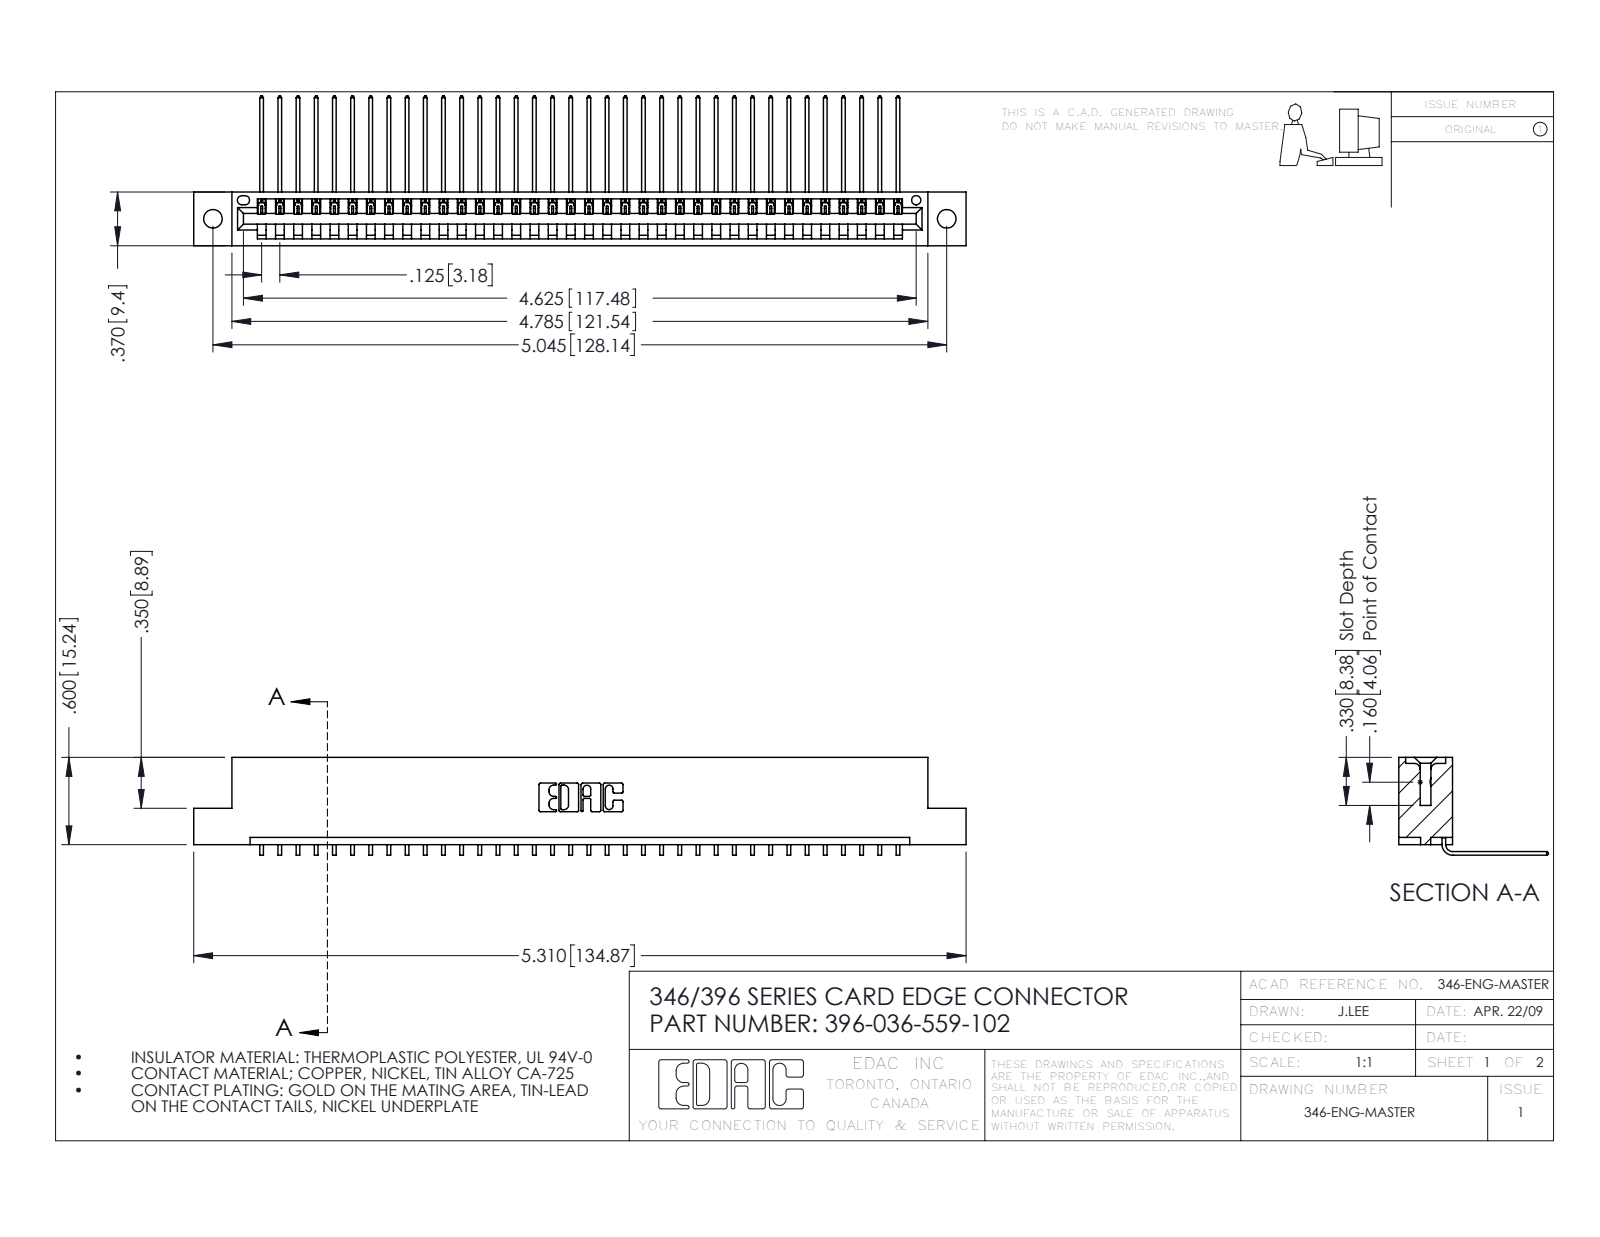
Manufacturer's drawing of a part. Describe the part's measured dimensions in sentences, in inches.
The part is named "346 Part_Flush Mounting Lugs - 0.128 Dia; 396-036-559-102; 345-292-001_558 559 Tail - 1". Its 3-D file was written by "SolidWorks 2016 (CONFIG_CONTROL_DESIGN)". It is 37 solids with 2282 faces: 1588 planar, 694 cylindrical and 0 other. Overall it measures 5.31 by 1.03 by 0.673 inches. Its volume is 0.79 cubic inches and its surface area 25.68 square inches. Round holes: 2 of diameter 0.128, 1 of diameter 0.064. Partial cylindrical surfaces (rounded edges, fillets, slot ends): 72 of radius 0.006, 22 of radius 0.01, 6 of radius 0.007, 6 of radius 0.031, 3 of radius 0.026, 2 of radius 0.031, 2 of radius 0.04, 1 of radius 0.014. The main face-to-face distances are 0.048, 0.322, 0.37, 0.25, 0.025, 0.072, 0.298, 0.148, 0.222, 0.1. The hole center spacings are 0.246, 4.836, 5.045.
